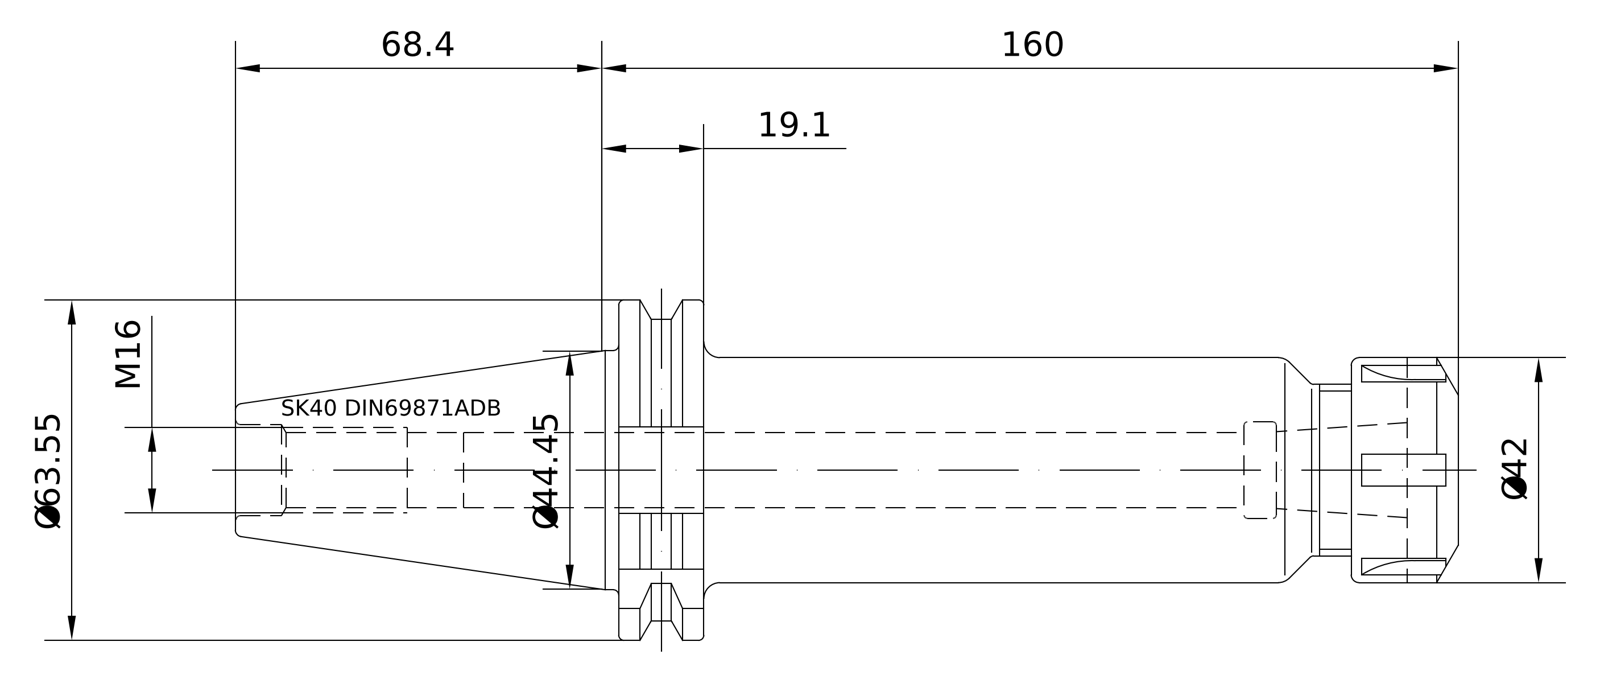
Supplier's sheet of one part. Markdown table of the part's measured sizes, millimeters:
| quantity | value |
| --- | --- |
| part name | 40-322-25; 83-912-25; 40-322-25_ASM |
| STEP written by | PRO/ENGINEER BY PARAMETRIC TECHNOLOGY CORPORATION, 2010430 (CONFIG_CONTROL_DESIGN) |
| units | millimeters |
| bodies | 2 solids, 143 faces (41 planar, 28 cylindrical, 74 other) |
| overall size | 228.25 × 63.52 × 61.42 |
| volume | 285 523 mm³ |
| surface area | 43 642 mm² |
| round holes (diameter × count) | 13.84 × 1, 17.01 × 1, 17.5 × 1, 18 × 1 |
| round bosses / shafts (diameter × count) | 43.75 × 1, 42 × 1, 32 × 1, 16.01 × 1 |
| partial cylindrical surfaces (radius × count) | 1.35 × 1, 28 × 1, 31.76 × 1 |
| main face-to-face distances | 136.8, 15.85, 120.95, 156.8, 140.95, 20, 144.8, 128.95, 8, 12 |
